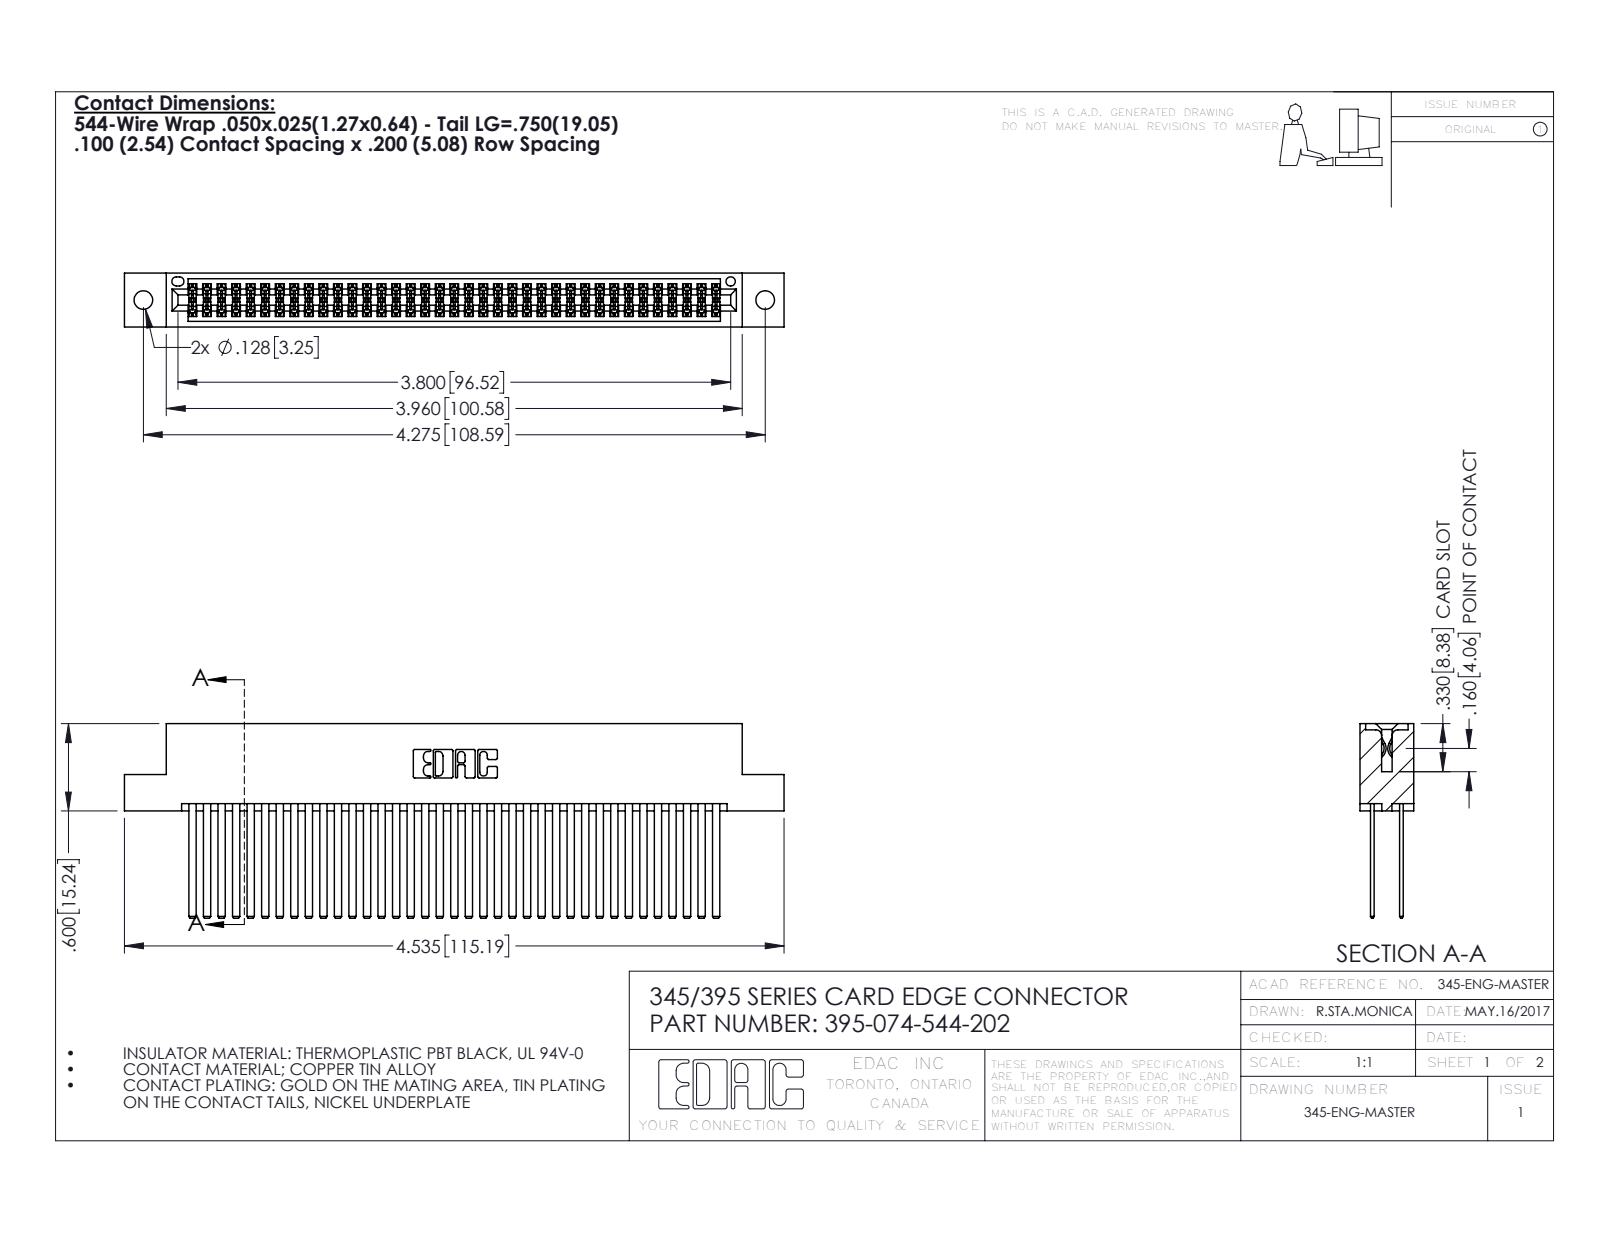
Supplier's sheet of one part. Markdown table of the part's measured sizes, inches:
| quantity | value |
| --- | --- |
| part name | 345-292-001_345-293-144; 345 Part_Flush Mounting Lugs - 0.128 Dia; 395-074-544-202 |
| STEP written by | SolidWorks 2016 (CONFIG_CONTROL_DESIGN) |
| units | inches |
| bodies | 75 solids, 3382 faces (2226 planar, 1156 cylindrical, 0 other) |
| overall size | 4.535 × 1.337 × 0.37 |
| volume | 0.741 in³ |
| surface area | 31.96 in² |
| round holes (diameter × count) | 0.128 × 2, 0.064 × 1 |
| partial cylindrical surfaces (radius × count) | 0.006 × 111, 0.01 × 22, 0.007 × 6, 0.031 × 6, 0.026 × 3, 0.014 × 2, 0.019 × 2, 0.022 × 2 |
| main face-to-face distances | 0.2, 0.025, 0.298, 0.072, 0.098, 0.272, 0.225, 0.175, 0.37, 0.05 |
| hole center spacings | 0.27, 4.039, 4.275 |
